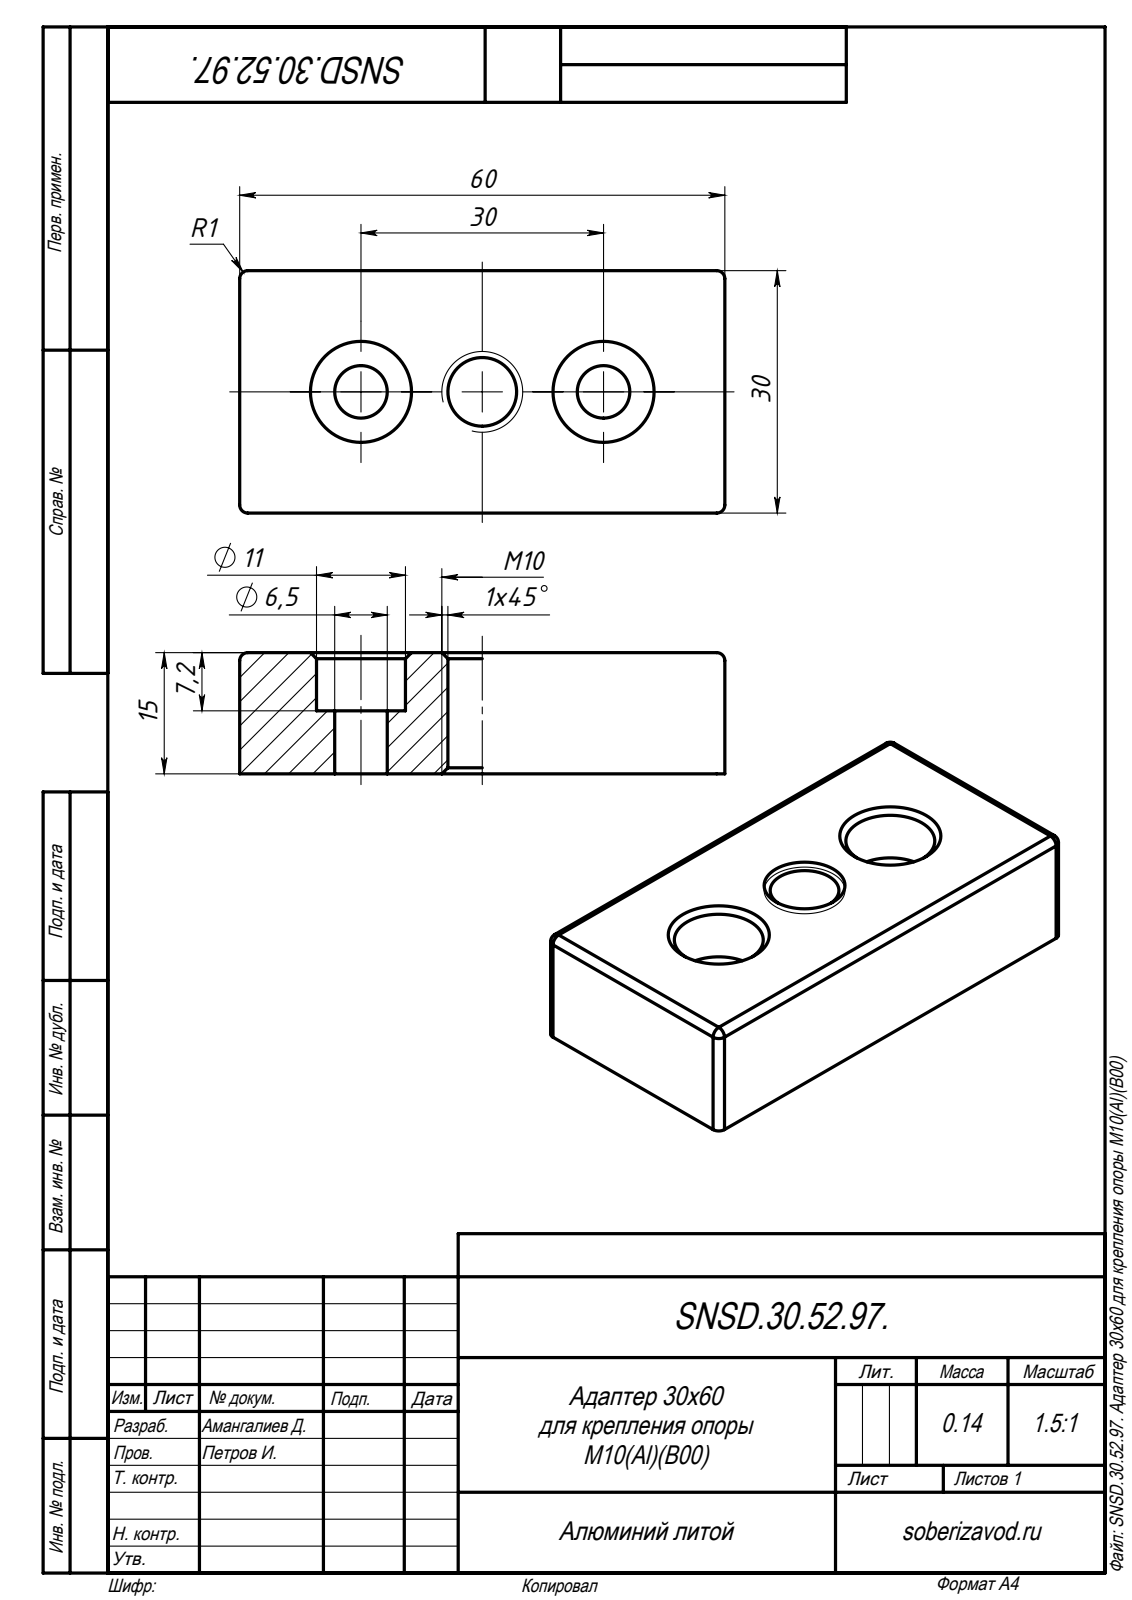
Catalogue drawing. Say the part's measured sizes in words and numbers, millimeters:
Its 3-D file was written by "SolidWorks 2014 (AUTOMOTIVE_DESIGN)". It is 1 solid with 102 faces: 44 planar, 46 cylindrical and 12 other. Overall it measures 60 by 30 by 15 millimeters. Its volume is 18 205 cubic millimeters and its surface area 10 421 square millimeters. Round holes: 2 of diameter 6.5, 2 of diameter 11, 1 of diameter 8.5. Partial cylindrical surfaces (rounded edges, fillets, slot ends): 8 of radius 1, 8 of radius 2.5, 2 of radius 8.5, 1 of radius 9.5. The main face-to-face distances are 3, 15, 27, 30, 12, 24, 57, 60, 13.5, 54. The hole center spacings are 15, 30.
